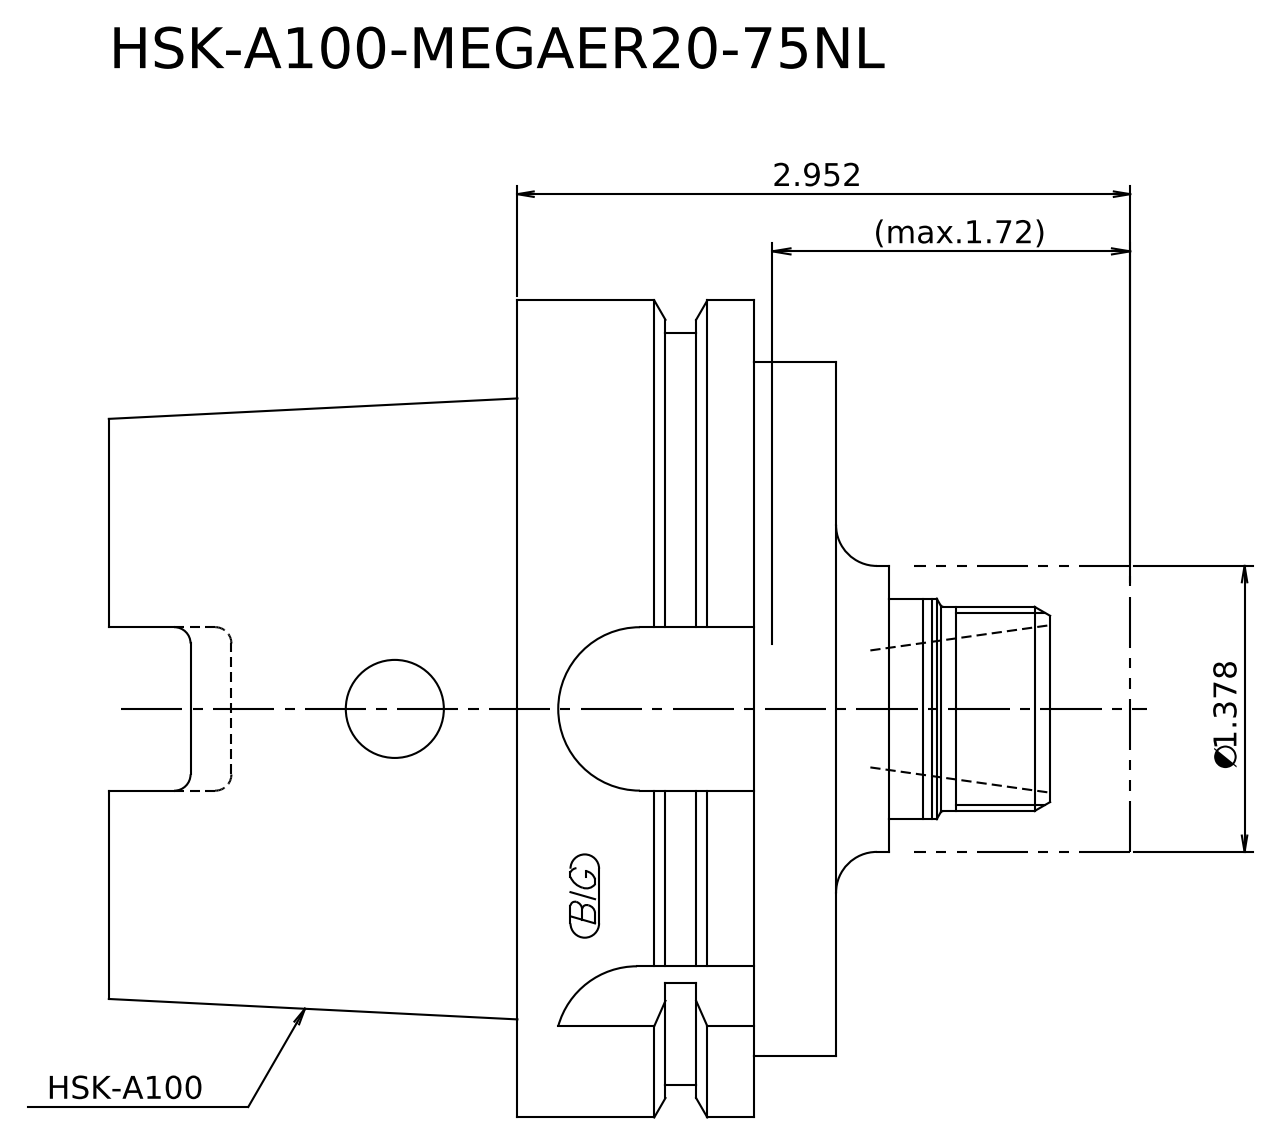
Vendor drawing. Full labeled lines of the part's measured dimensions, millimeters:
STEP written by: Kubotek KeyCreator 2011 V10.0.2 (22737) (automotive_design)
Units: millimetres
Bodies: 2 solids, 24 faces (10 planar, 8 cylindrical, 6 other)
Overall size (bounding box): 125 × 100 × 100
Volume: 534 550 mm³ · Surface area: 46 900 mm²
Round bosses / shafts (diameter × count): ⌀100 ×1, ⌀92 ×1, ⌀85 ×1, ⌀35 ×1, ⌀27 ×1, ⌀25 ×1
Main face-to-face distances: 89, 39, 50, 10, 29, 79, 9.5, 19.5, 48.5, 98.5
